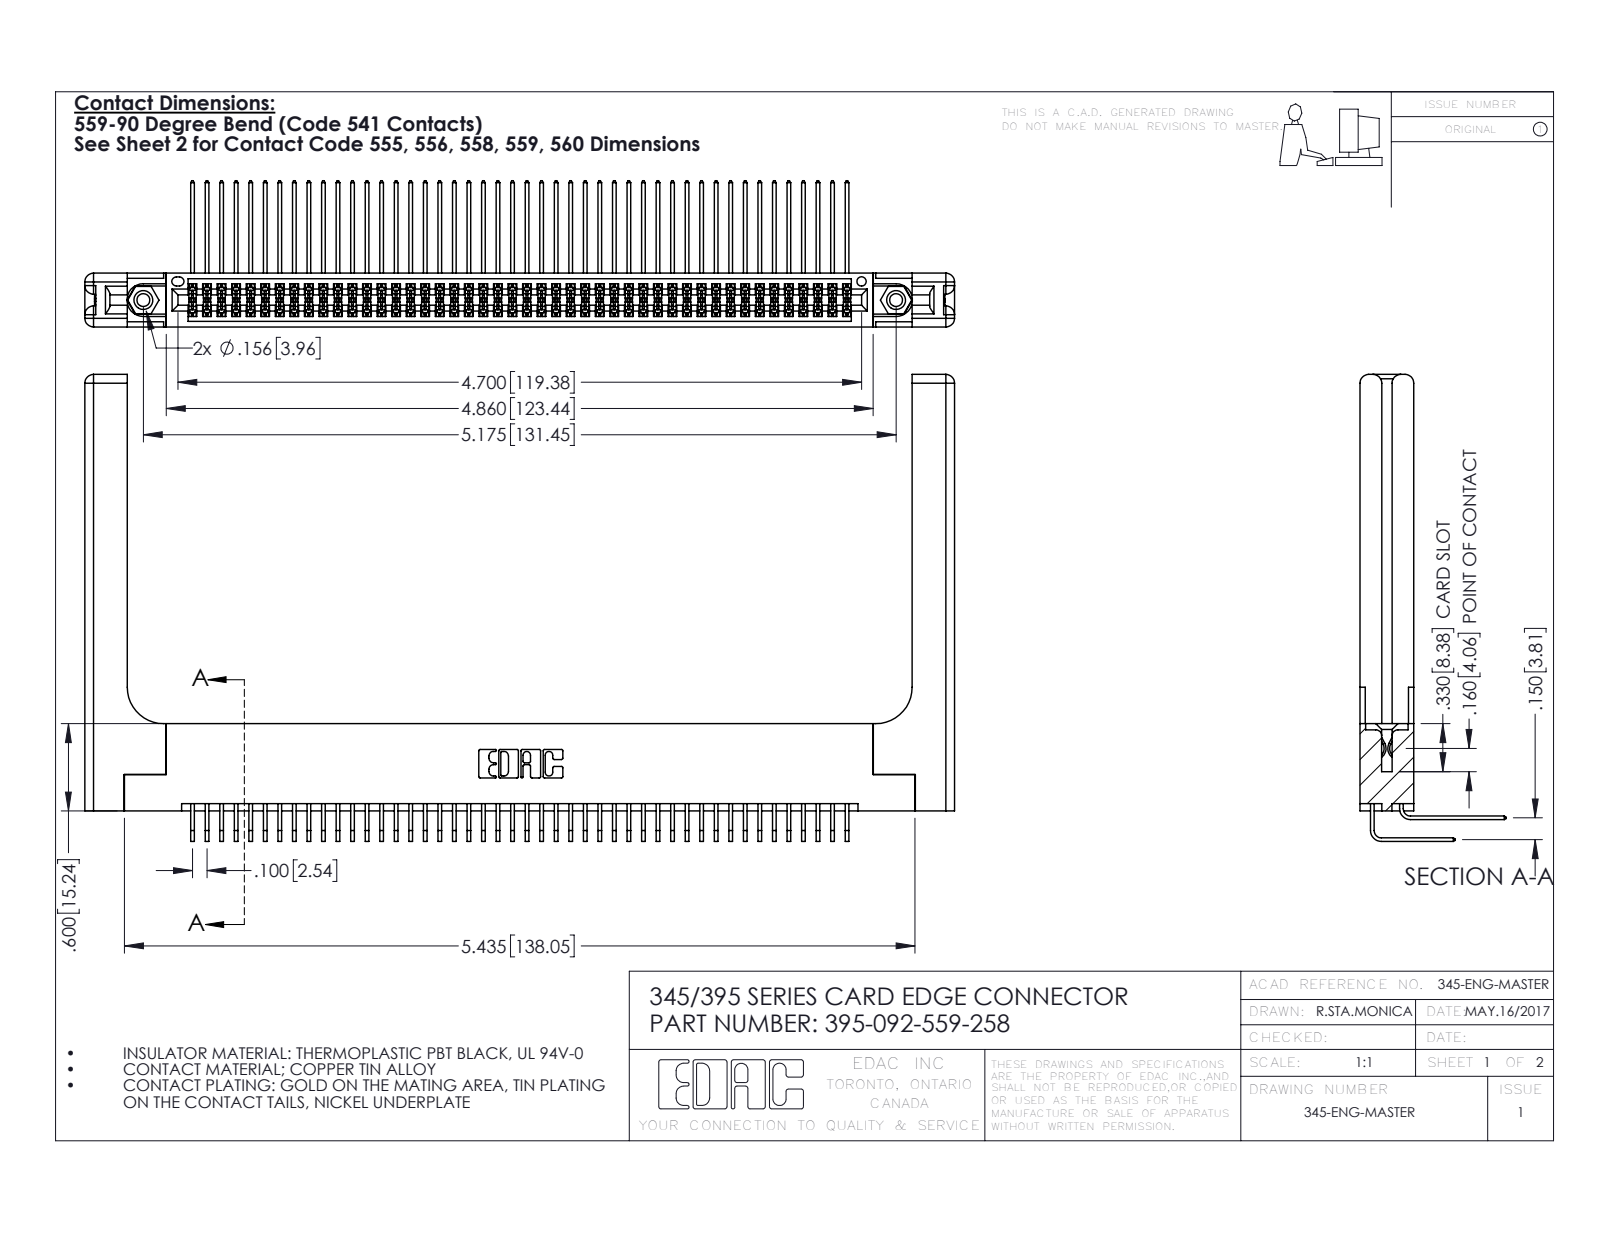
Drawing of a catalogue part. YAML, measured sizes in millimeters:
part_name: "345-292-001_558 559 Tail - 1; 345 Part_Flush Mounting Lugs - 0.156 Dia-TH; 395-092-559-258; 345-292-001_559 Tail - 2 (+2 more)"
step_written_by: "SolidWorks 2016 (CONFIG_CONTROL_DESIGN)"
units: millimeters
bodies: {solids: 97, faces: 5166, planar: 3448, cylindrical: 1658, other: 60}
overall_size: [151.9, 81.5, 25.5]
volume: 23790
surface_area: 30280
round_holes:
  - {diameter: 2.3, count: 2}
  - {diameter: 3.2, count: 2}
  - {diameter: 4, count: 2}
  - {diameter: 1.6, count: 1}
round_bosses_or_shafts:
  - {diameter: 3.9, count: 2}
partial_cylinders:
  - {radius: 0.2, count: 138}
  - {radius: 0.3, count: 22}
  - {radius: 1.5, count: 16}
  - {radius: 0.2, count: 6}
  - {radius: 0.8, count: 6}
  - {radius: 0.7, count: 3}
  - {radius: 0.4, count: 2}
  - {radius: 0.5, count: 2}
face_to_face_distances: [1.8, 7.6, 9.4, 5.1, 2.5, 6.9, 0.6, 5.7, 4.4, 3.8]
hole_center_spacings: [6.9, 125.5, 131.4]
